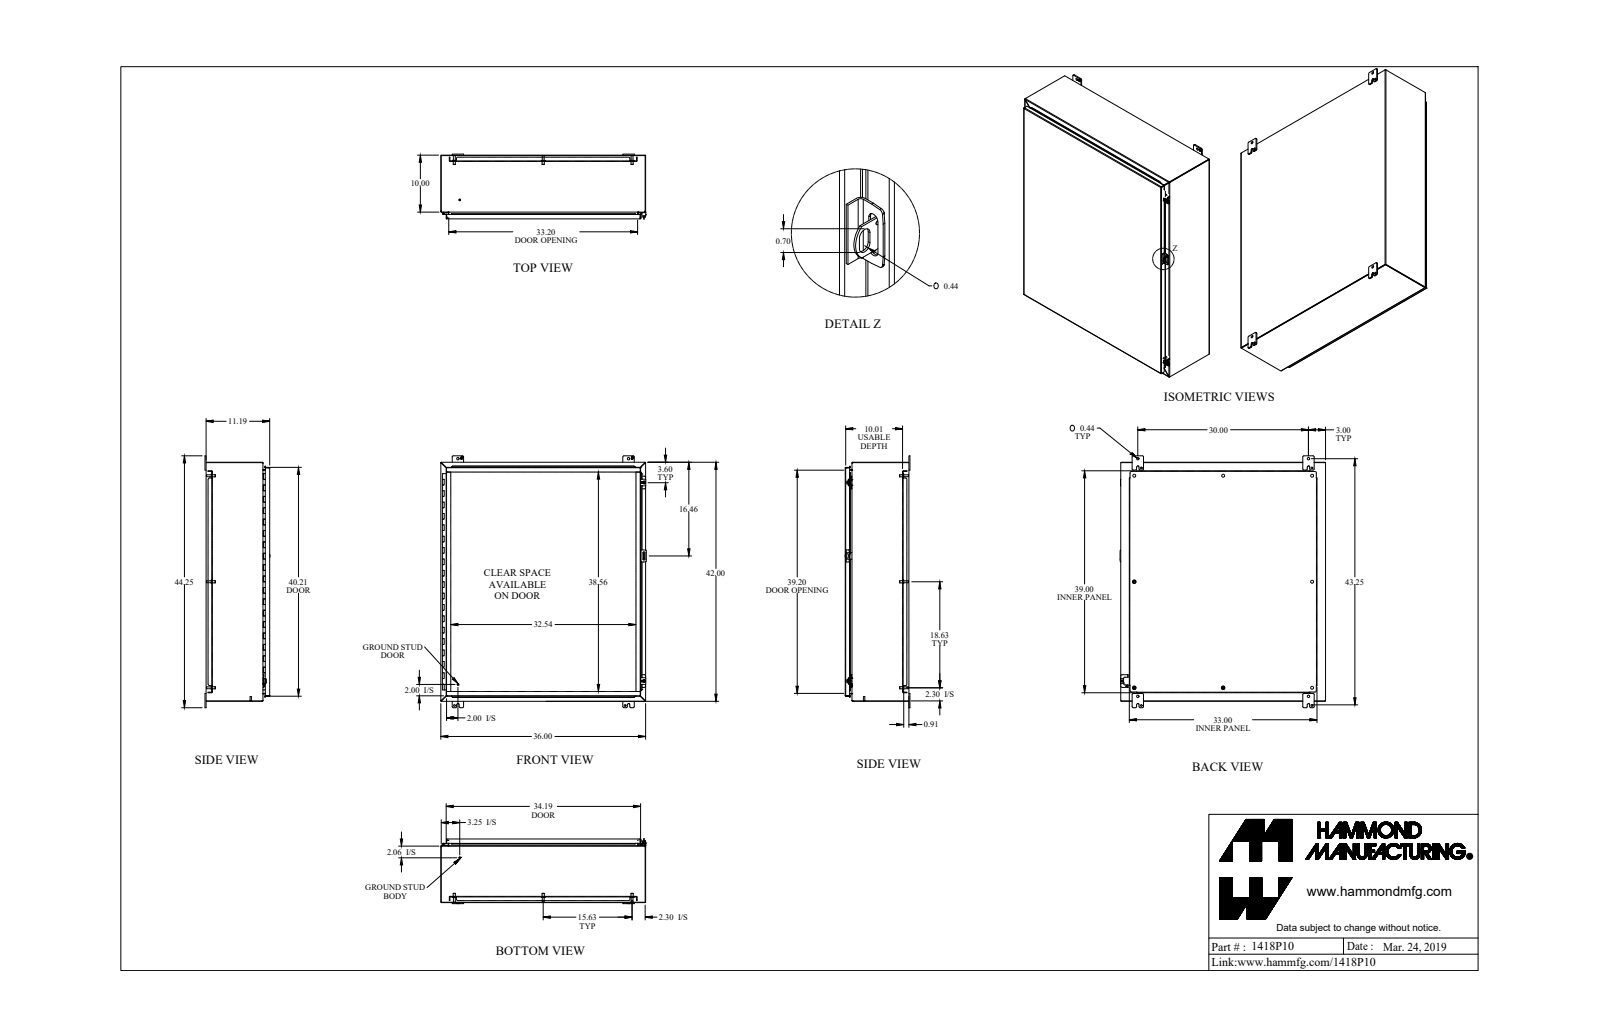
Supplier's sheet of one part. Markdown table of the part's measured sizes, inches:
| quantity | value |
| --- | --- |
| part name | 1418P10_Default |
| STEP written by | SolidWorks 2019 (CONFIG_CONTROL_DESIGN) |
| units | inches |
| bodies | 52 solids, 1548 faces (883 planar, 556 cylindrical, 109 other) |
| overall size | 44.25 × 36.125 × 11.437 |
| volume | 548.2 in³ |
| surface area | 14 227 in² |
| round holes (diameter × count) | 0.5 × 8, 0.307 × 4, 0.313 × 4, 0.437 × 4, 0.445 × 4, 0.213 × 2, 0.265 × 2, 0.375 × 2, 0.125 × 1, 0.187 × 1 |
| round bosses / shafts (diameter × count) | 0.65 × 8, 0.375 × 8, 0.33 × 8, 1 × 4, 0.5 × 2, 0.39 × 2, 0.281 × 2, 0.25 × 2 |
| partial cylindrical surfaces (radius × count) | 0.188 × 37, 0.036 × 22, 0.108 × 22, 0.25 × 20, 0.116 × 16, 0.048 × 13, 0.143 × 13, 0.04 × 8 |
| main face-to-face distances | 0.072, 11.113, 11.041, 11.185, 0.095, 0.937, 1.009, 10.081, 10.009, 1.032 |
| hole center spacings | 15.625, 18.625, 30, 31.25, 36.38, 37.25, 40.394, 1.735 |
